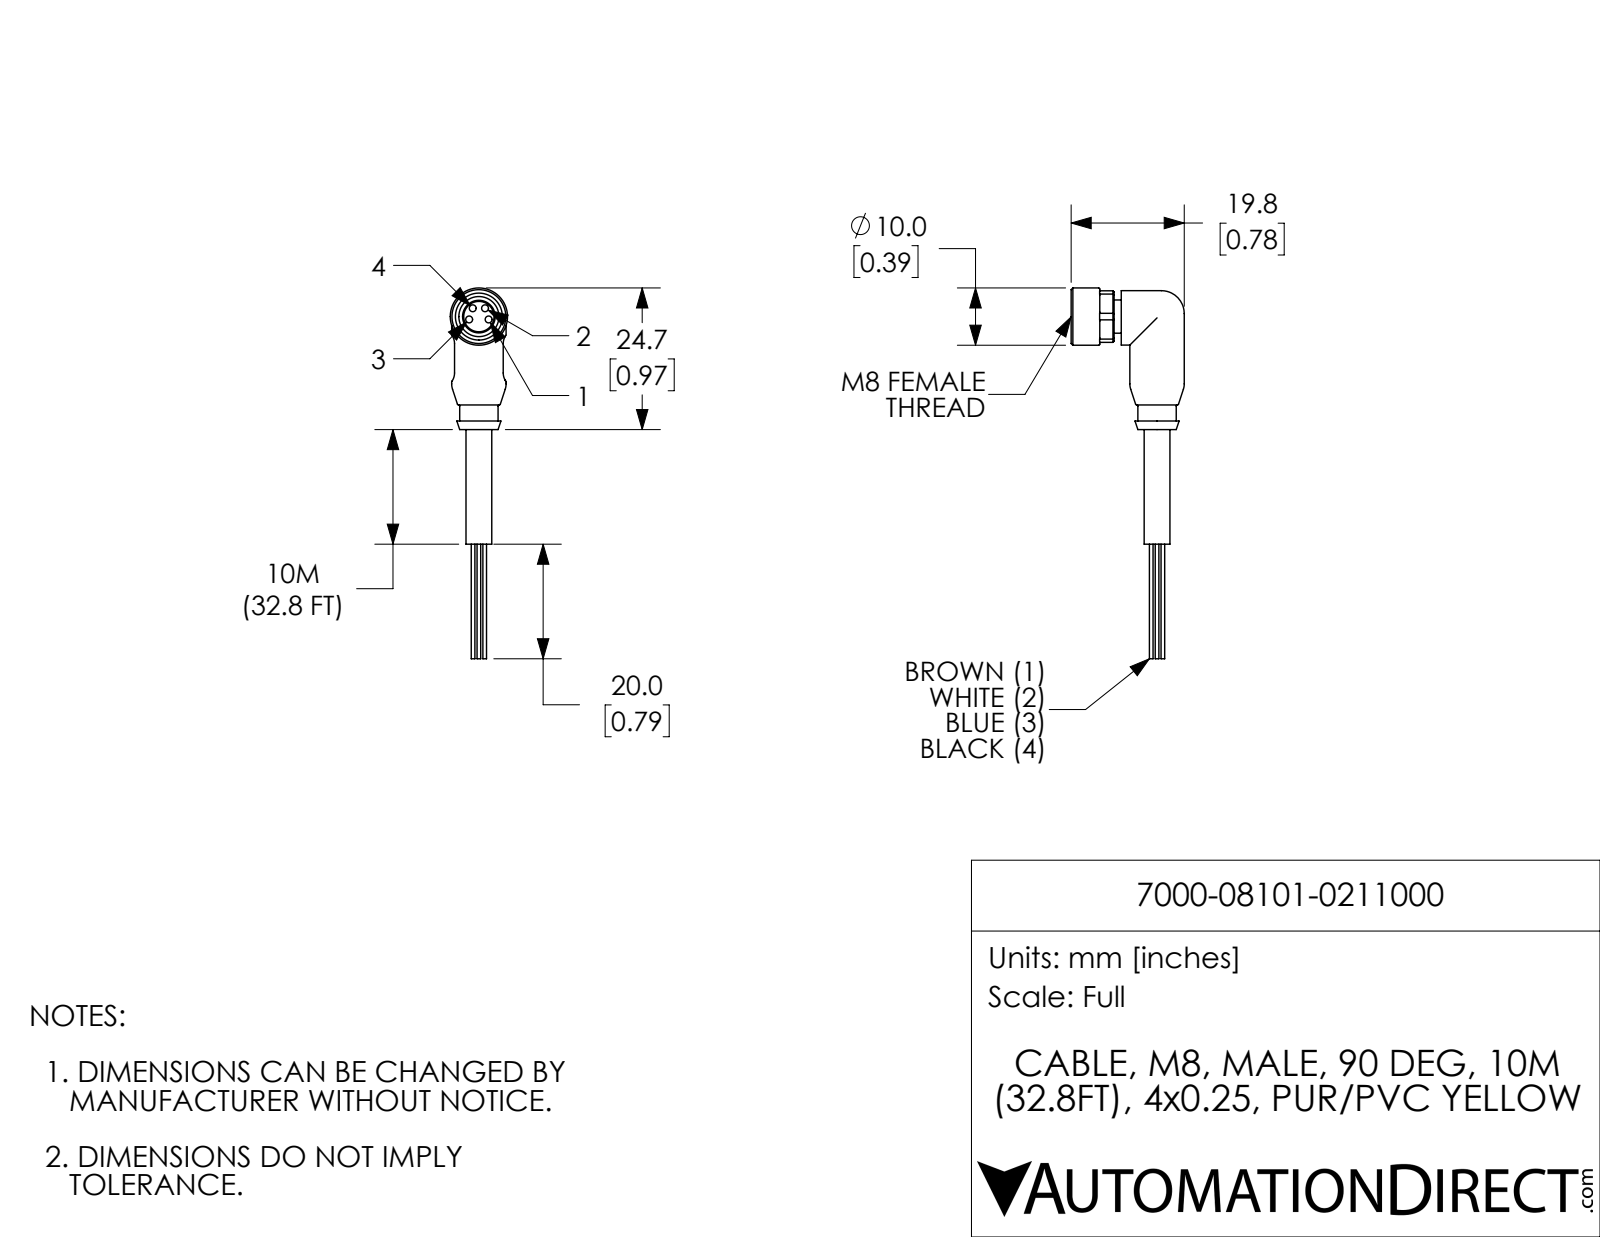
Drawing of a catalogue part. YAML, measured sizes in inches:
part_name: "7000-08101-0211000"
step_written_by: "SolidWorks 2017 (AUTOMOTIVE_DESIGN)"
units: inches
bodies: {solids: 5, faces: 117, planar: 41, cylindrical: 47, other: 29}
overall_size: [2.548, 0.778, 0.394]
volume: 0.147
surface_area: 2.976
round_holes:
  - {diameter: 0.047, count: 4}
  - {diameter: 0.276, count: 1}
round_bosses_or_shafts:
  - {diameter: 0.025, count: 3}
  - {diameter: 0.374, count: 2}
  - {diameter: 0.394, count: 1}
  - {diameter: 0.264, count: 1}
  - {diameter: 0.228, count: 1}
  - {diameter: 0.224, count: 1}
  - {diameter: 0.177, count: 1}
  - {diameter: 0.025, count: 1}
partial_cylinders:
  - {radius: 0.008, count: 4}
  - {radius: 0.098, count: 4}
  - {radius: 0.193, count: 1}
face_to_face_distances: [0.049, 0.354, 0.059, 0.335, 0.028, 0.787, 0.268, 0.317, 0.295, 0.344]
hole_center_spacings: [0.07, 0.071, 0.081, 0.133, 0.084, 0.134]
